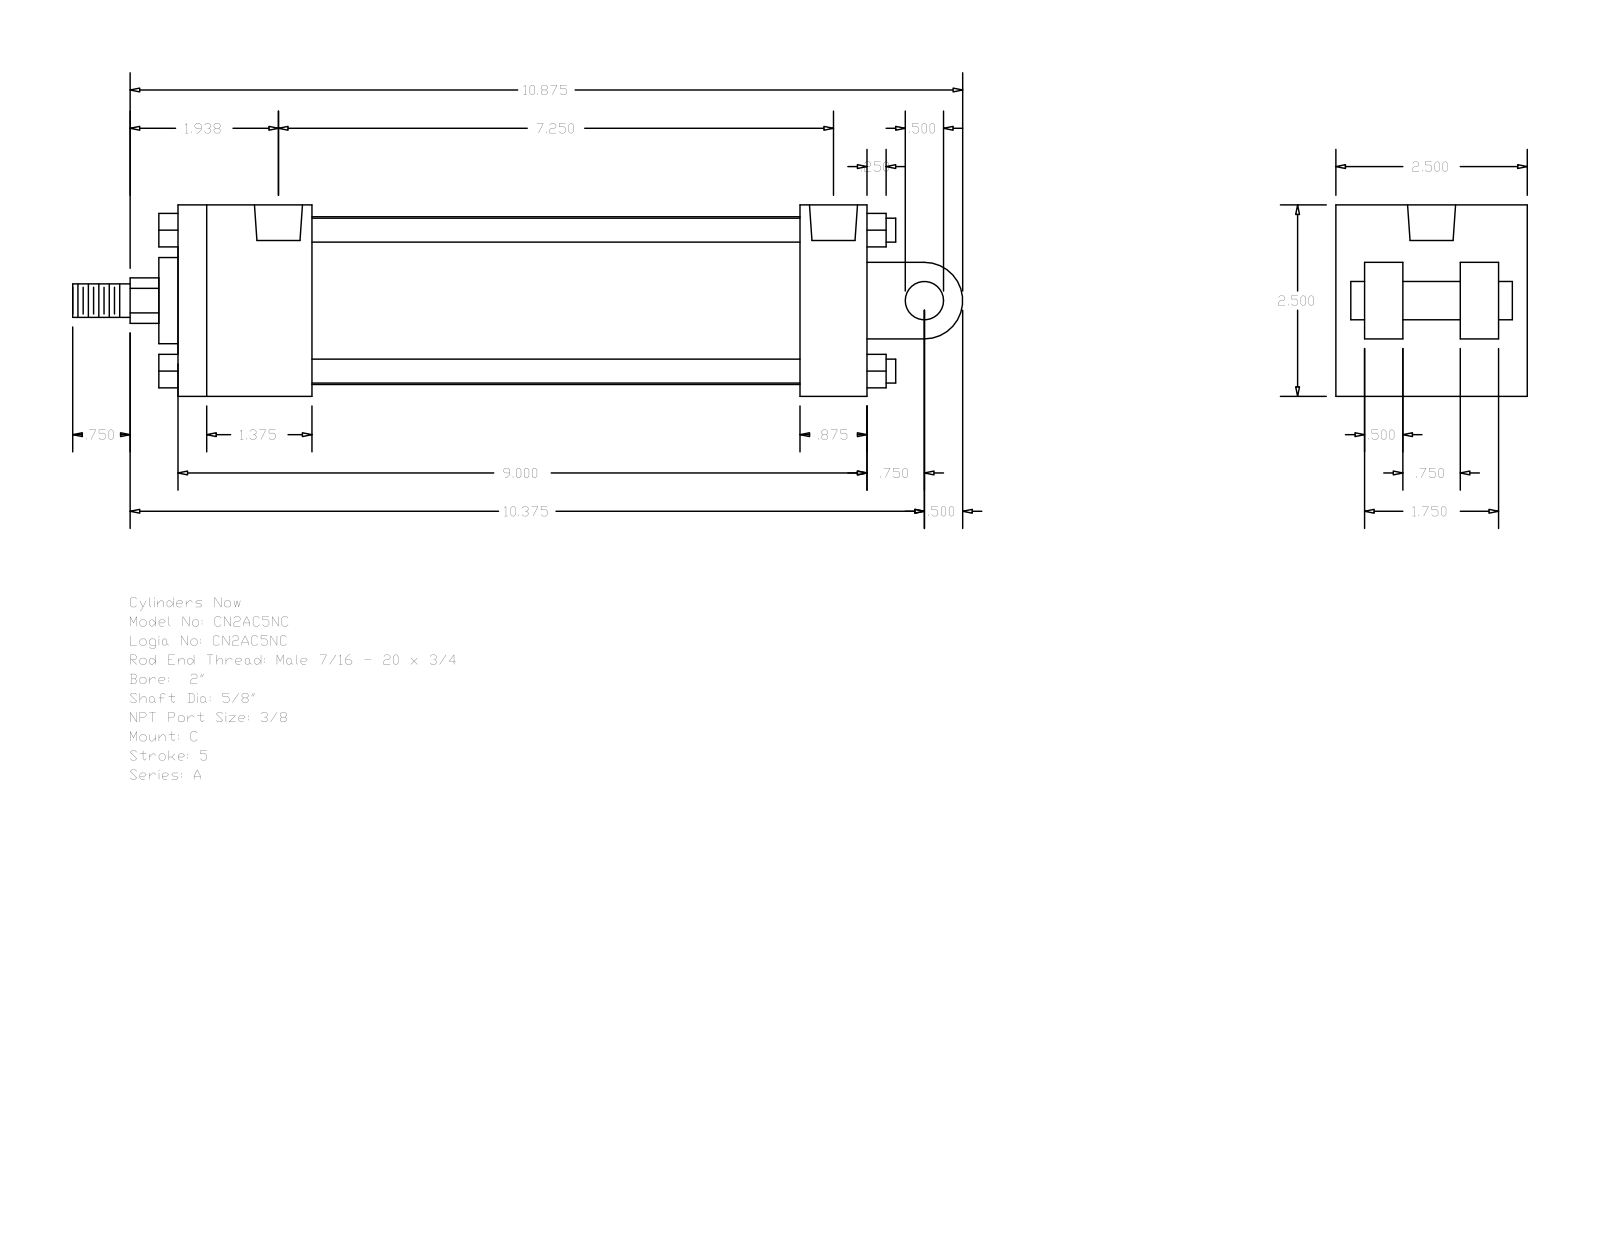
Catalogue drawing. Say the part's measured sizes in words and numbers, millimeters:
The part is named "A_C__0200_0.625". Its 3-D file was written by "GSSL Pune (CONFIG_CONTROL_DESIGN)". It is 0 solids with 135 faces: 102 planar, 33 cylindrical and 0 other. Overall it measures 295.27 by 63.5 by 63.5 millimeters. Round holes: 4 of diameter 5.56, 2 of diameter 15.93. Round bosses or shafts: 4 of diameter 7.94, 1 of diameter 55.63, 1 of diameter 28.57, 1 of diameter 15.88, 1 of diameter 12.7, 1 of diameter 11.11. Partial cylindrical surfaces (rounded edges, fillets, slot ends): 1 of radius 7.54, 1 of radius 12.7. The main face-to-face distances are 63.5, 228.59, 22.22, 44.45, 184.14, 206.37, 161.92, 12.7, 6.35, 53.98. The hole center spacings are 176.2, 3.97, 3.98, 180.17, 180.18, 184.15.
